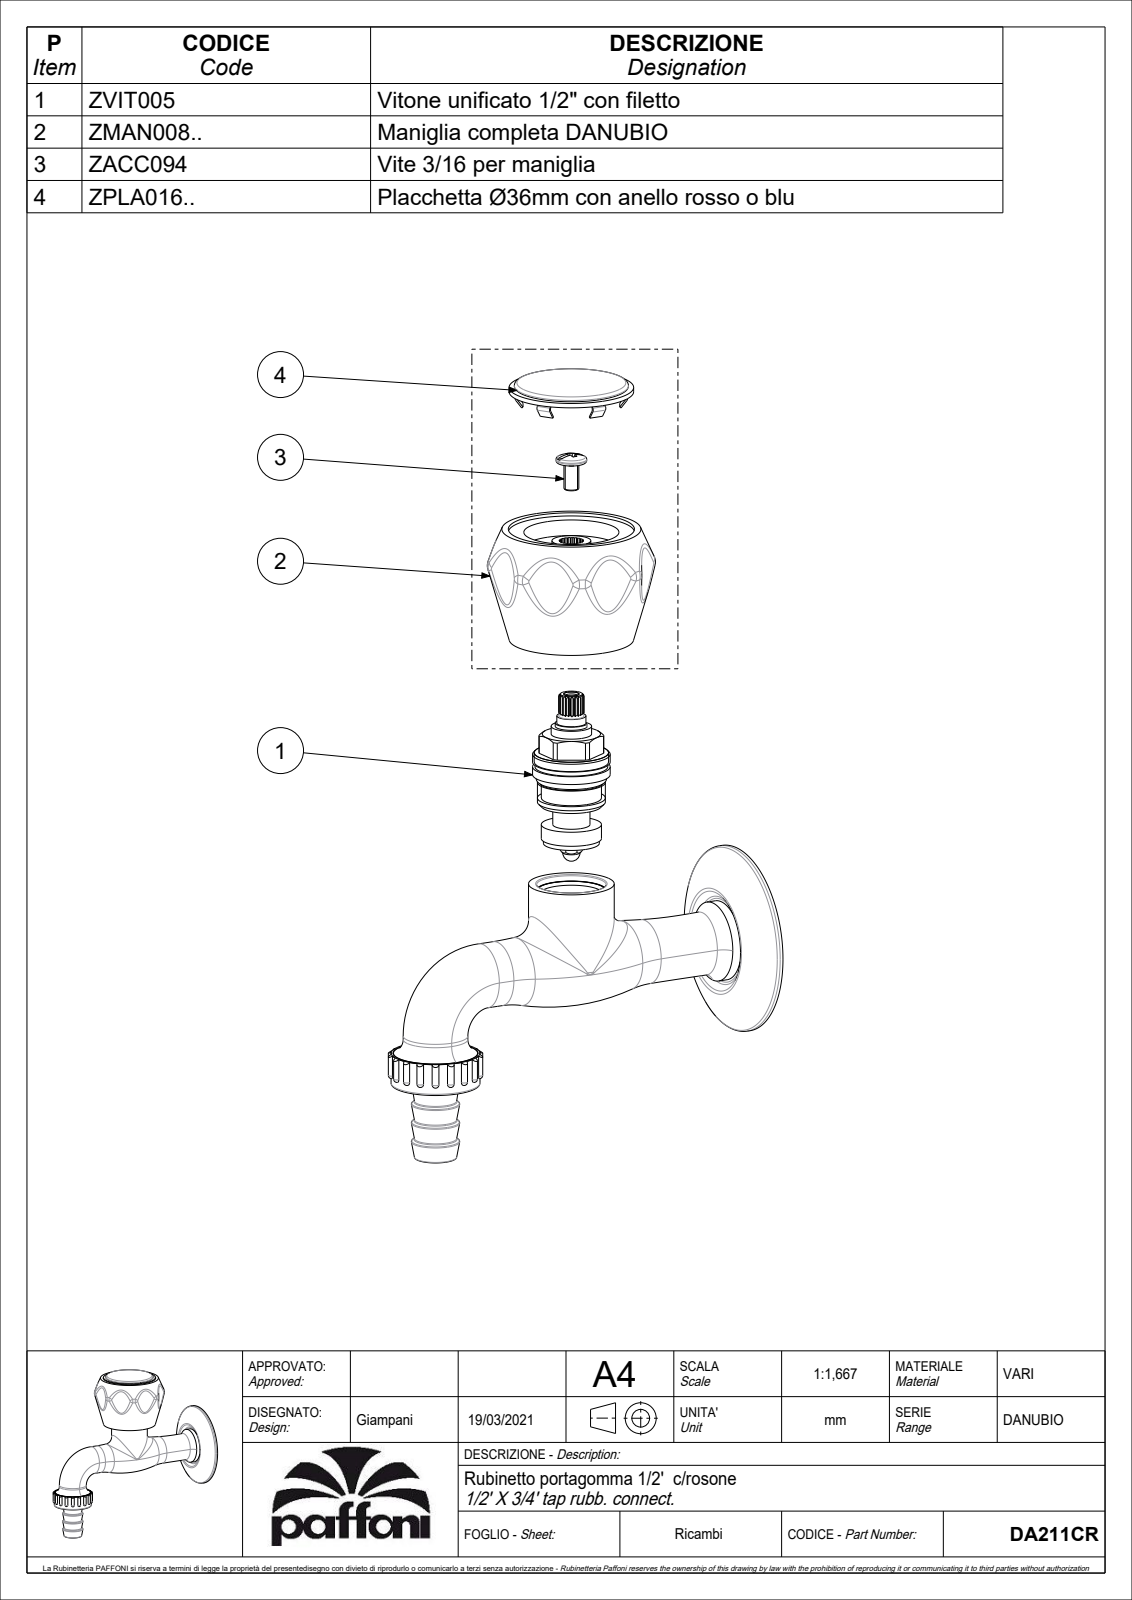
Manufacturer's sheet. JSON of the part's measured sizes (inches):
{"part_name": "DA211CR", "step_written_by": "CREO PARAMETRIC BY PTC INC, 2020044 (CONFIG_CONTROL_DESIGN)", "units": "inches", "bodies": {"solids": 1, "faces": 206, "planar": 9, "cylindrical": 38, "other": 159}, "overall_size": [5.11, 4.655, 2.283], "volume_in3": 8.37, "surface_area_in2": 38.83, "round_bosses_or_shafts": [[2.283, 1], [1.516, 1], [1.083, 1], [1.043, 1], [0.972, 1], [0.827, 1]], "partial_cylinders_radius": [[0.041, 18], [0.839, 8]], "face_to_face_distances": [2.207, 3.596, 1.39, 0.303, 3.612, 1.406, 0.016, 0.925, 3.131, 4.521]}
